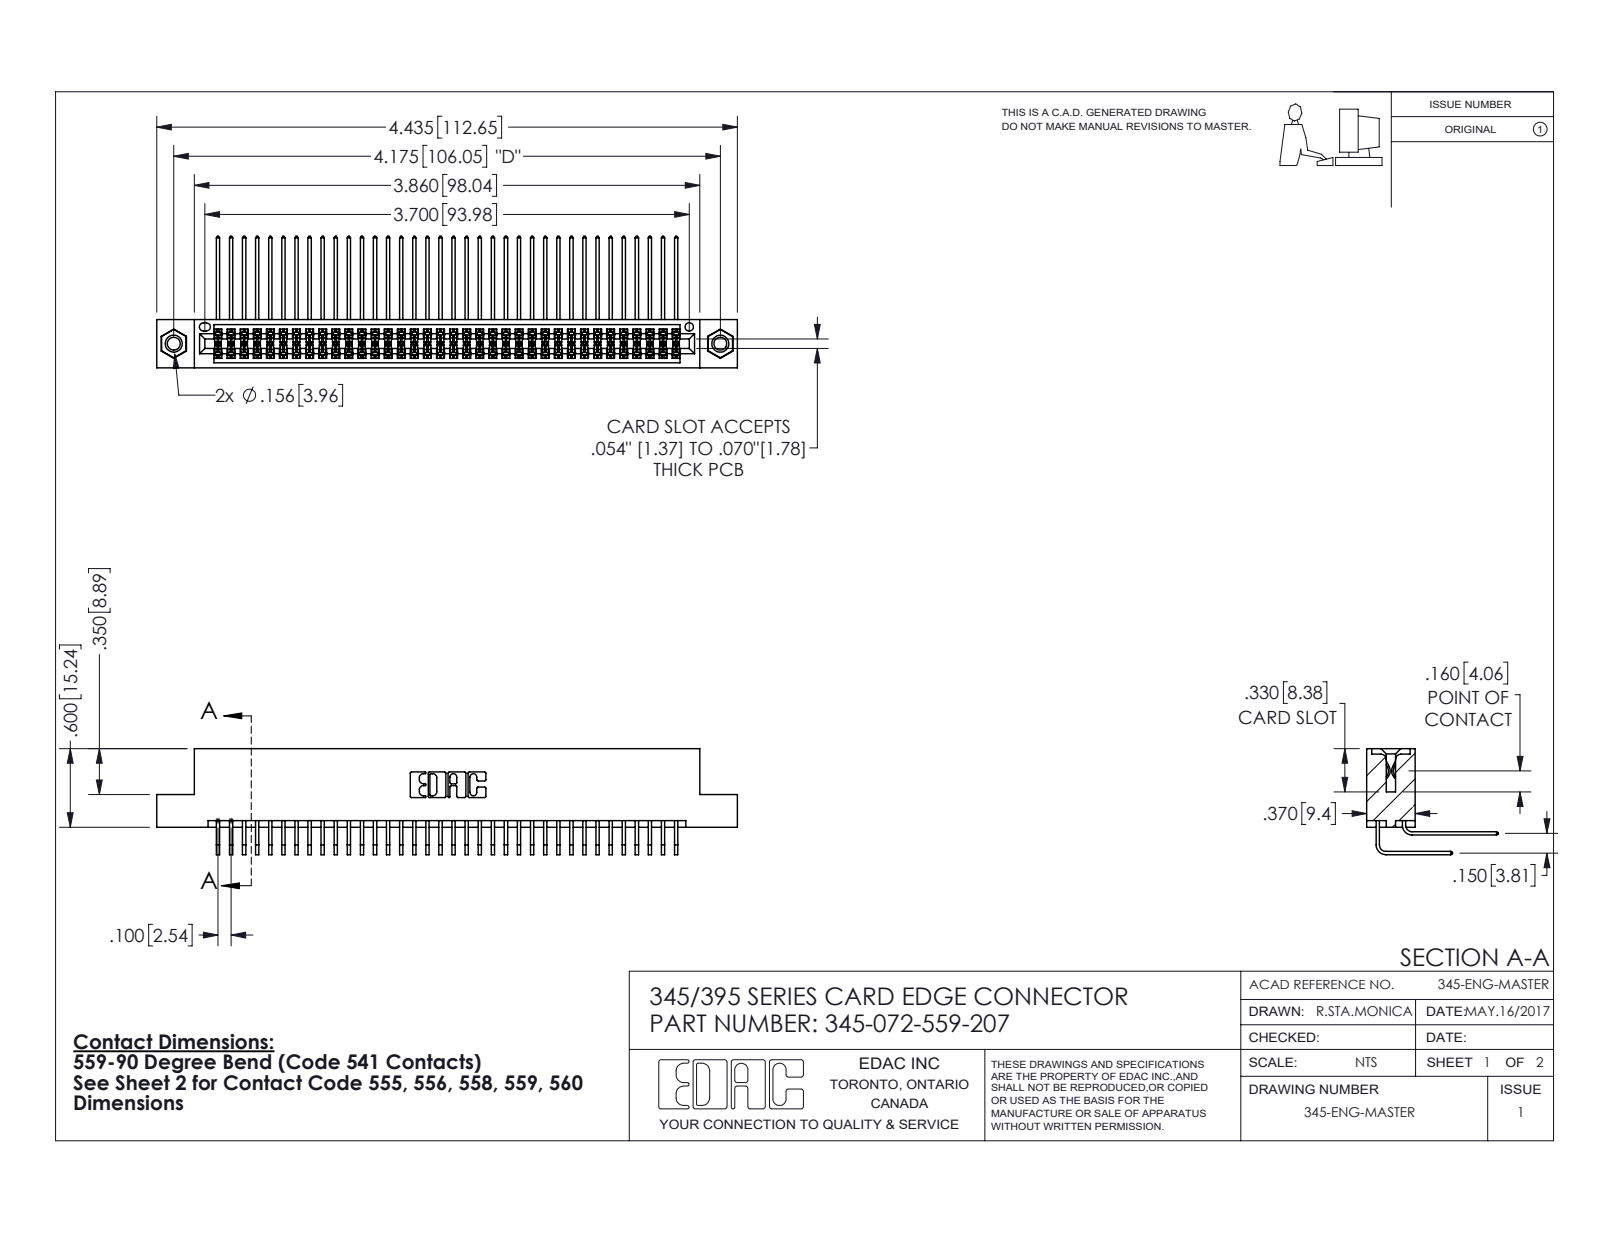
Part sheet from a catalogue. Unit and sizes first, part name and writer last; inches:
Units: inches
Overall size (bounding box): 4.435 × 1.005 × 0.809
Round holes (diameter × count): ⌀0.098 ×2, ⌀0.125 ×2, ⌀0.156 ×2, ⌀0.064 ×1
Round bosses / shafts (diameter × count): ⌀0.155 ×2
Partial cylindrical surfaces — rounded edges, fillets, slot ends (radius × count): R0.006 ×143, R0.01 ×22, R0.007 ×6, R0.031 ×6, R0.026 ×3, R0.014 ×2, R0.019 ×2, R0.022 ×2
Main face-to-face distances: 0.072, 0.298, 0.2, 0.37, 0.098, 0.272, 0.025, 0.225, 0.175, 0.15
Hole centre spacings: 0.27, 3.939, 4.175
Volume: 0.689 in³ · Surface area: 28.76 in²
Bodies: 75 solids, 3930 faces (2632 planar, 1282 cylindrical, 16 other)
Part name (STEP PRODUCT): 345-292-001_559 Tail - 2; 345-292-001_558 559 Tail - 1; 345 Part_Flush Mounting Lugs - 0.156 Dia-TI; 345-250-001_345-250-005-103 (+1 more)
STEP written by: SolidWorks 2016 (CONFIG_CONTROL_DESIGN)
